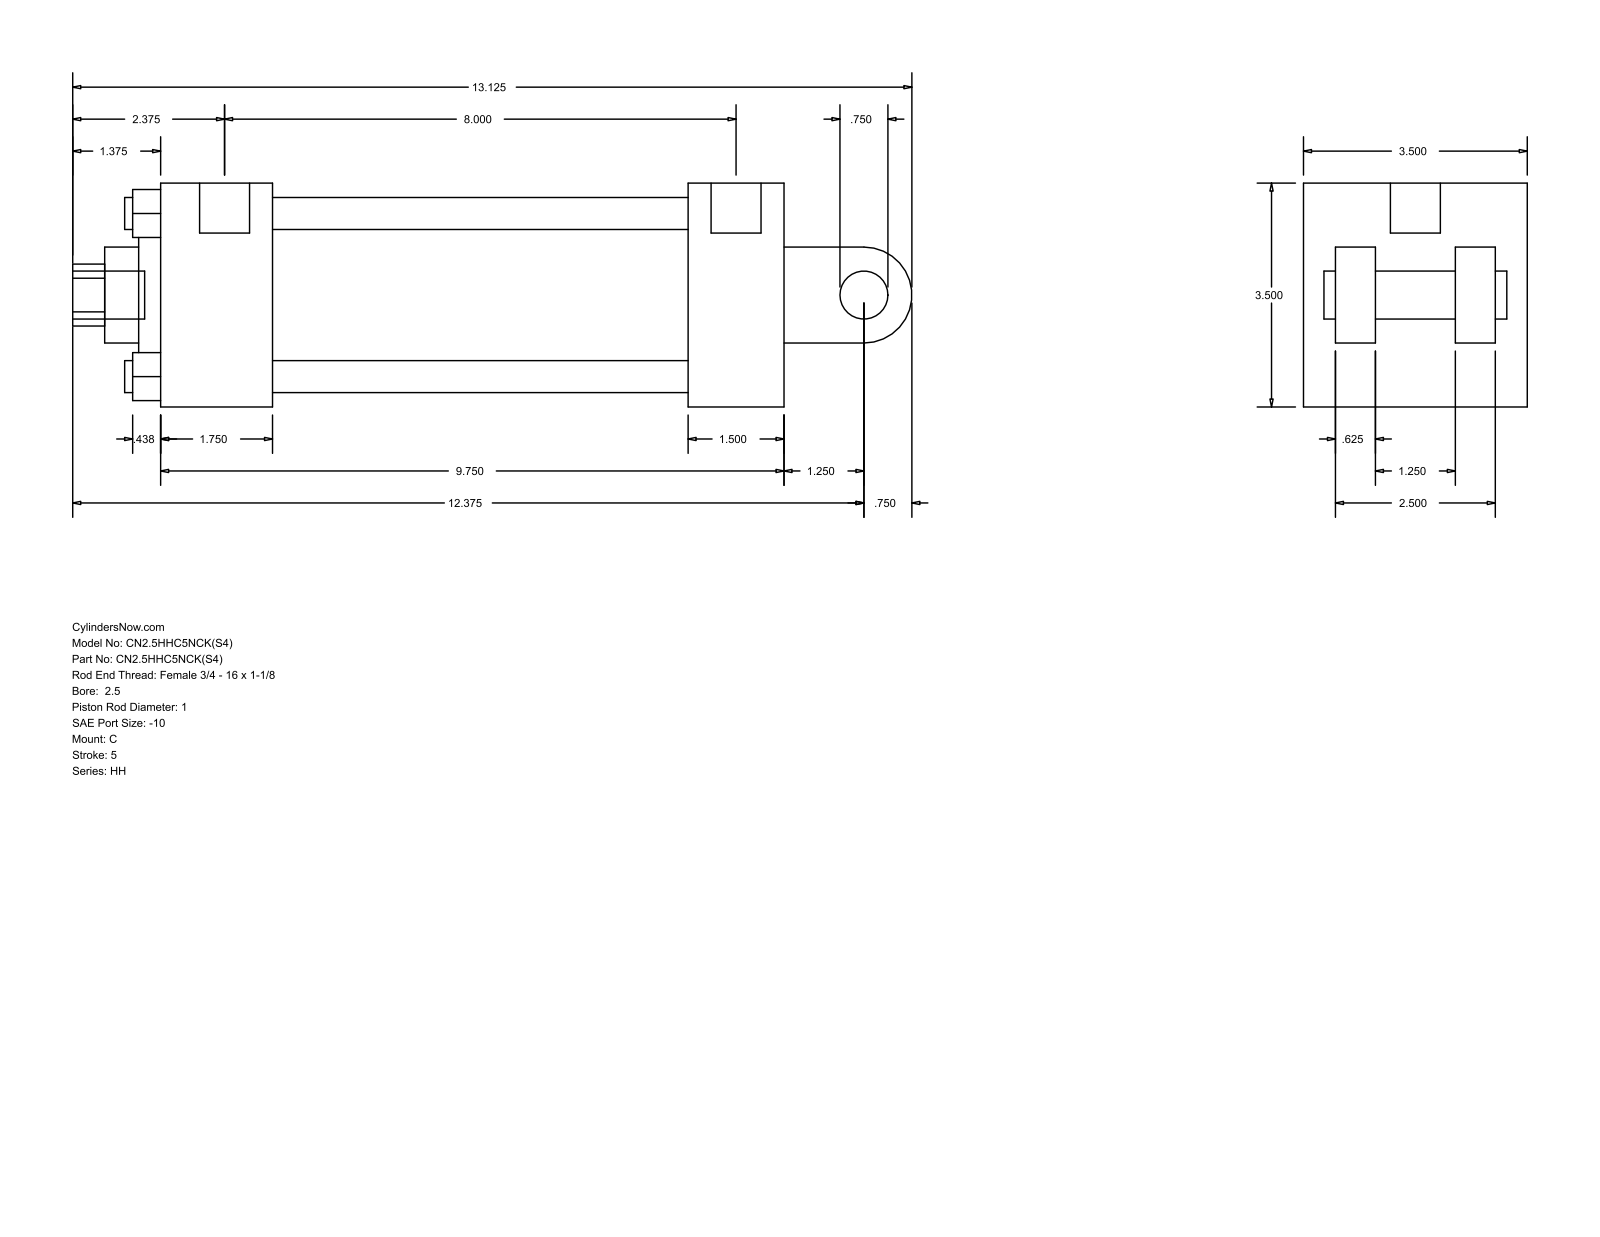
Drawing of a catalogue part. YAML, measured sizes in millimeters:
part_name: "HH_C__0250_1"
step_written_by: "GSSL Pune (CONFIG_CONTROL_DESIGN)"
units: millimeters
bodies: {solids: 0, faces: 101, planar: 71, cylindrical: 30, other: 0}
overall_size: [333.38, 88.9, 88.9]
round_holes:
  - {diameter: 12.7, count: 4}
  - {diameter: 5.56, count: 2}
  - {diameter: 19.84, count: 1}
  - {diameter: 25.4, count: 1}
  - {diameter: 38.1, count: 1}
  - {diameter: 60.33, count: 1}
  - {diameter: 73.03, count: 1}
round_bosses_or_shafts:
  - {diameter: 19.05, count: 2}
  - {diameter: 5.56, count: 2}
  - {diameter: 19.84, count: 1}
partial_cylinders:
  - {radius: 12.29, count: 1}
  - {radius: 19.05, count: 1}
face_to_face_distances: [88.9, 38.1, 247.65, 63.5, 15.87, 209.55, 44.46, 165.09, 203.19, 12.7]
hole_center_spacings: [45.79, 64.76, 91.58, 1.59]
